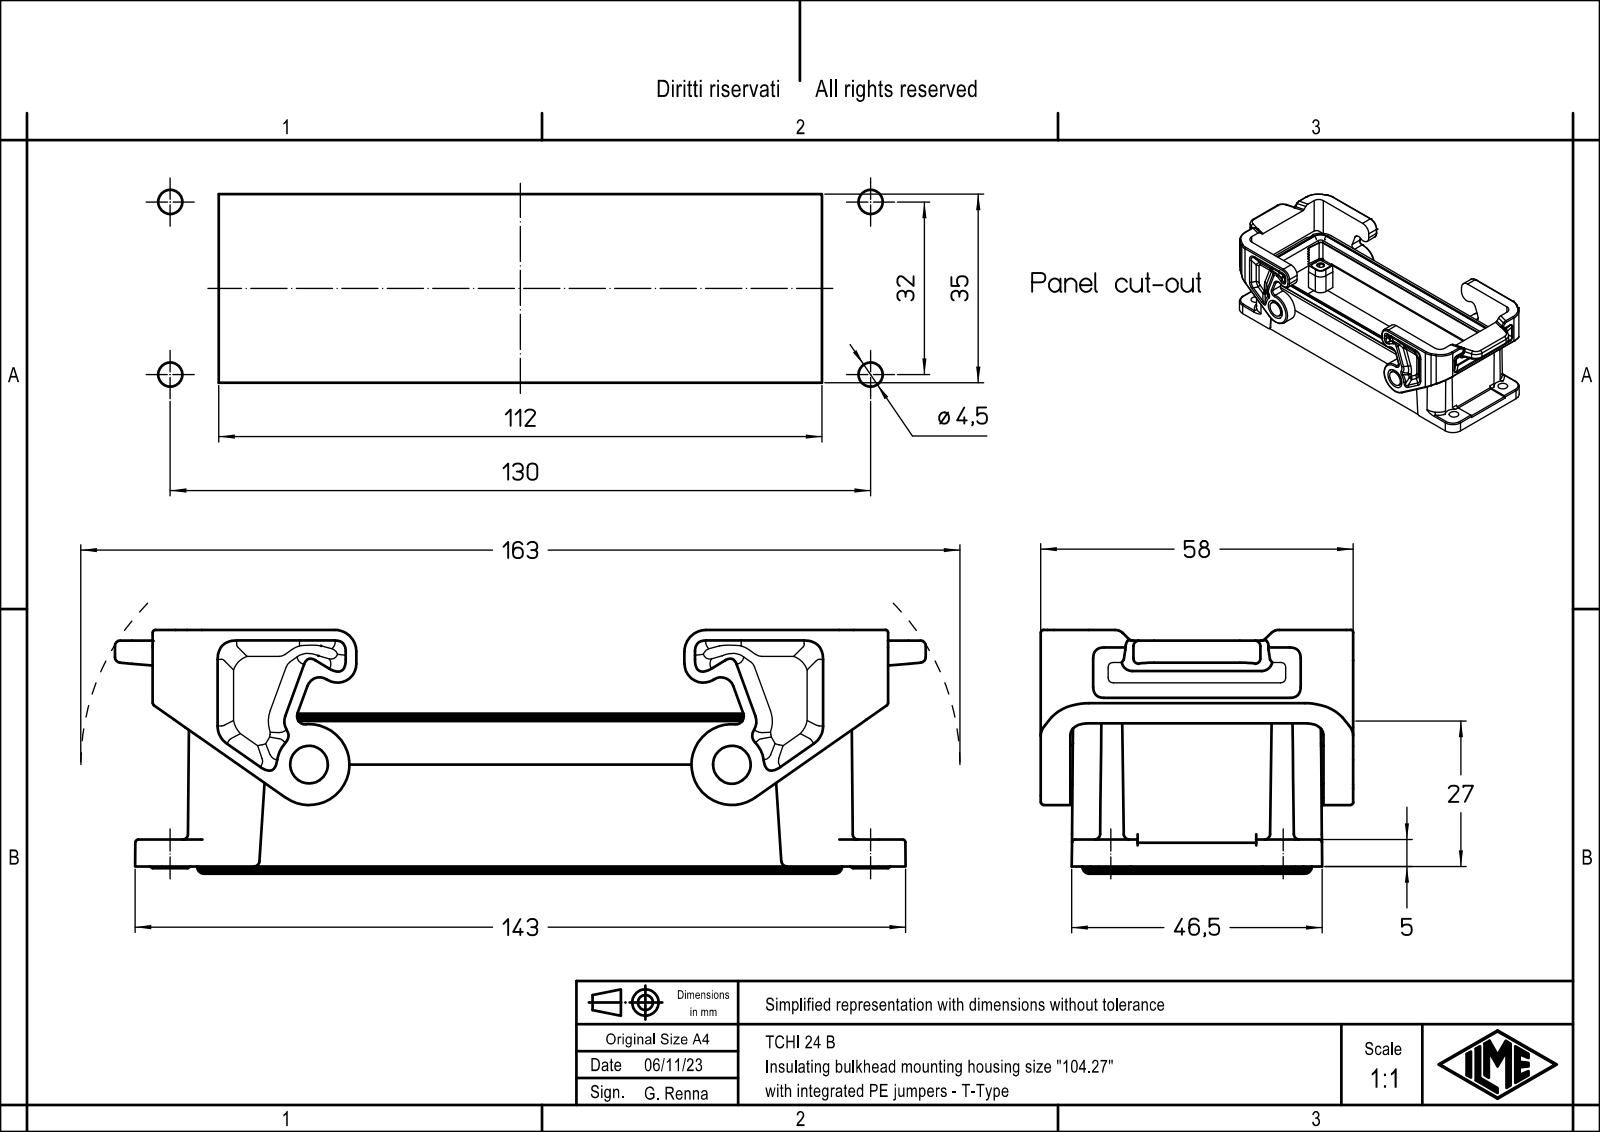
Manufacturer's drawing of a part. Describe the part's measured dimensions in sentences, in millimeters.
The part is named "TCHI 24 B". Its 3-D file was written by "Creo Elements/Direct Modeling 20.1B 02-Apr-2019 (C) Parametric Technology GmbH (AUTOMOTIVE_DESIGN)". It is 1 solid with 906 faces: 466 planar, 256 cylindrical and 184 other. Overall it measures 150.5 by 58 by 45.25 millimeters. Its volume is 79 026 cubic millimeters and its surface area 46 506 square millimeters. Round holes: 4 of diameter 2.5, 4 of diameter 3.5, 4 of diameter 4.5, 2 of diameter 7.2. Round bosses or shafts: 4 of diameter 4.8, 2 of diameter 7. Partial cylindrical surfaces (rounded edges, fillets, slot ends): 28 of radius 1, 22 of radius 1.5, 20 of radius 1.3, 16 of radius 2, 12 of radius 3, 12 of radius 5.5, 10 of radius 2.7, 8 of radius 5. The main face-to-face distances are 5.9, 41.1, 35.2, 40.4, 34.5, 6.6, 6.3, 34.8, 0.7, 40.7. The hole center spacings are 13.24, 32.24, 117.03, 120.66, 27, 32, 104, 107.45.
